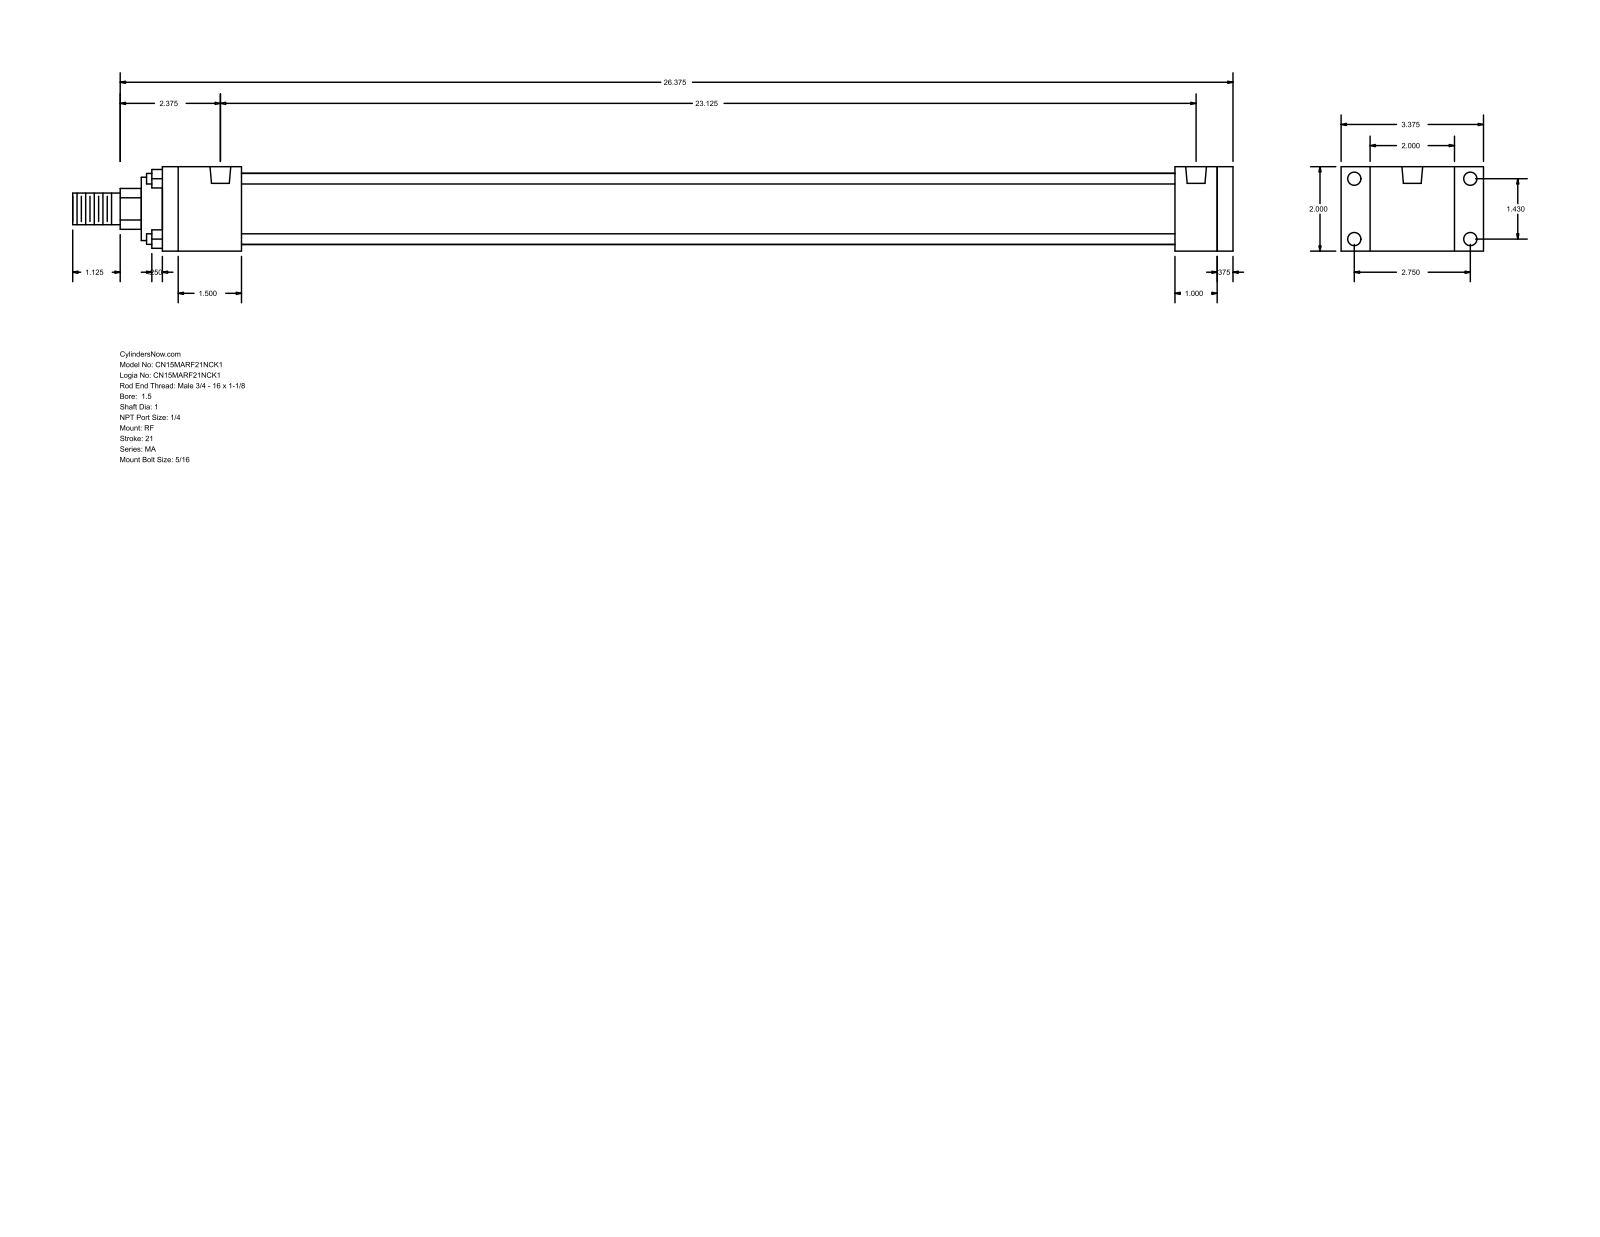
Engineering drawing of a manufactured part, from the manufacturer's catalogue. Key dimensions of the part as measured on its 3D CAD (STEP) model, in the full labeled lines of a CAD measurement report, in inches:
Part name (STEP PRODUCT): MA_RF__0150_1
STEP written by: GSSL Pune (CONFIG_CONTROL_DESIGN)
Units: inches
Bodies: 0 solids, 92 faces (64 planar, 28 cylindrical, 0 other)
Overall size (bounding box): 27.5 × 3.375 × 2
Round holes (diameter × count): ⌀0.313 ×8, ⌀0.492 ×2
Round bosses / shafts (diameter × count): ⌀0.25 ×4, ⌀1.69 ×1, ⌀1.5 ×1, ⌀1 ×1, ⌀0.75 ×1
Partial cylindrical surfaces — rounded edges, fillets, slot ends (radius × count): R0.484 ×1
Main face-to-face distances: 2, 0.375, 25.375, 25, 1, 24, 1.375, 1.875, 22.125, 23.125
Hole centre spacings: 1.43, 2.75, 3.099, 23.125
